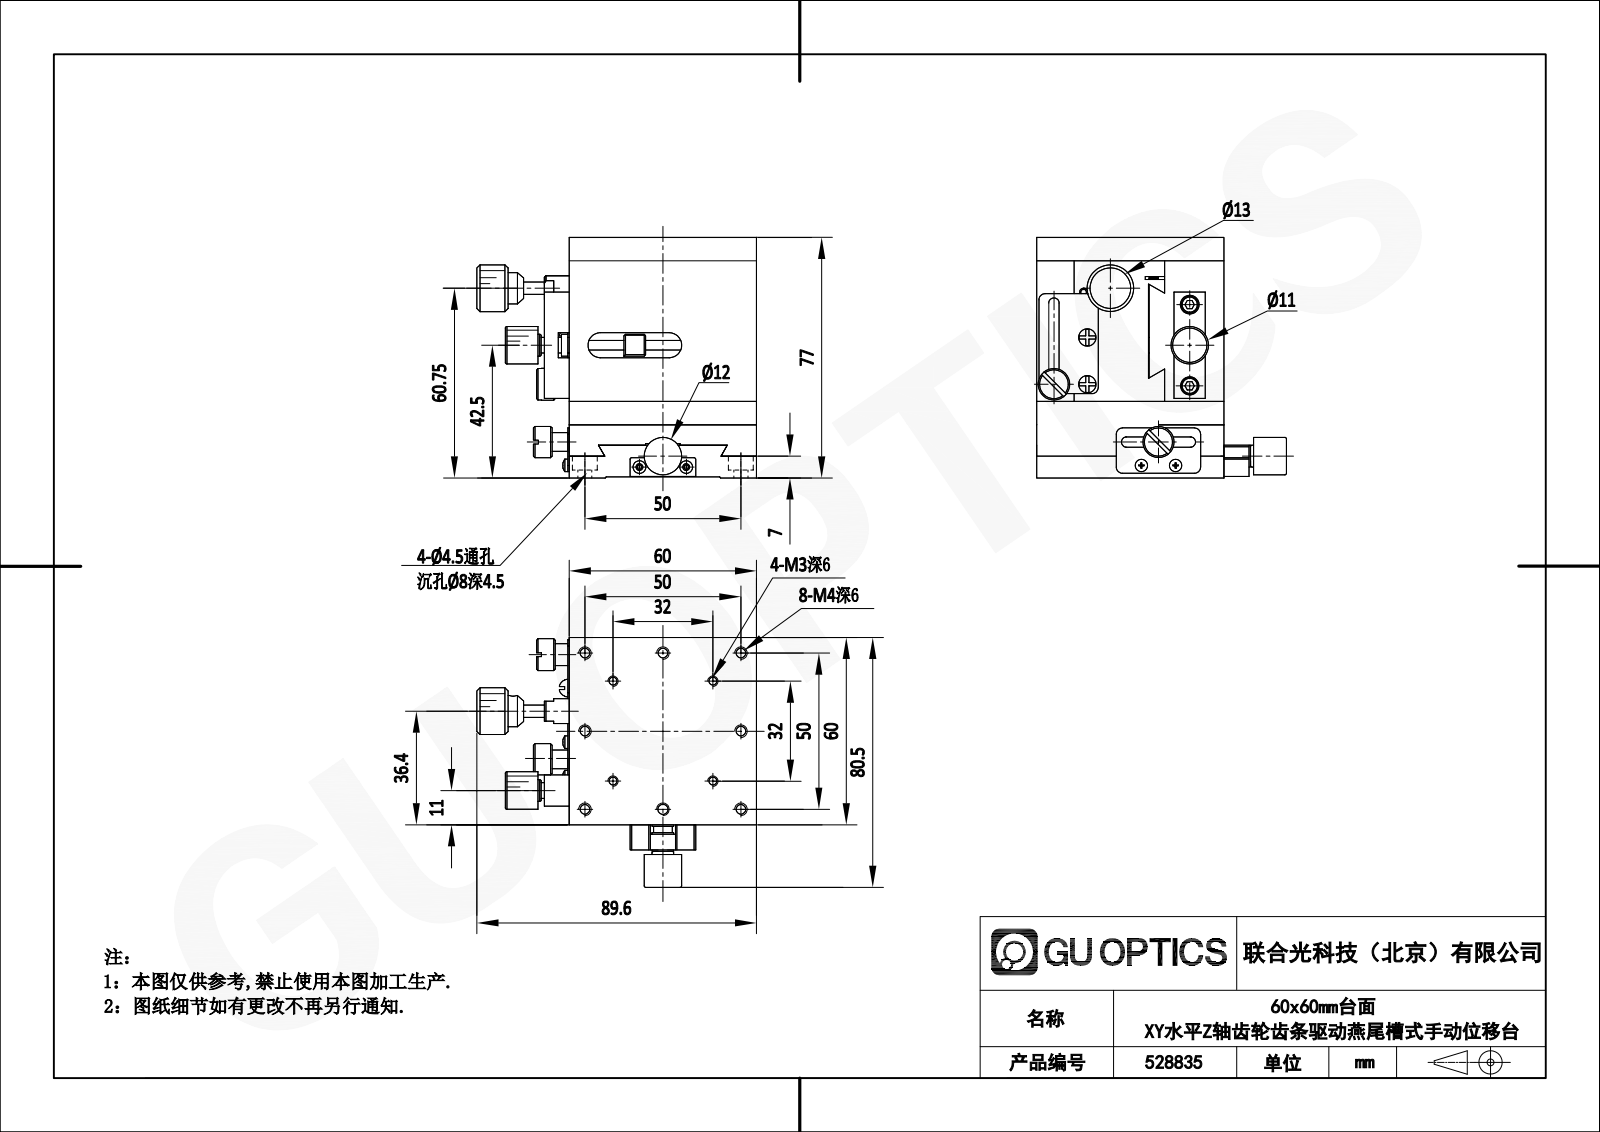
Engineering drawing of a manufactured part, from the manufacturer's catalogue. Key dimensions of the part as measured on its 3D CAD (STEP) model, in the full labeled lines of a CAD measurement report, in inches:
Part name (STEP PRODUCT): 528835
STEP written by: SolidWorks 2020 (CONFIG_CONTROL_DESIGN)
Units: inches
Bodies: 42 solids, 2534 faces (1478 planar, 392 cylindrical, 664 other)
Overall size (bounding box): 3.441 × 3.169 × 3.012
Volume: 16.17 in³ · Surface area: 153.9 in²
Round holes (diameter × count): ⌀0.098 ×35, ⌀0.13 ×13, ⌀0.177 ×9, ⌀0.315 ×8, ⌀0.161 ×7, ⌀0.236 ×7, ⌀0.134 ×5, ⌀0.114 ×4, ⌀0.244 ×4, ⌀0.063 ×2, ⌀0.081 ×2, ⌀0.122 ×2
Round bosses / shafts (diameter × count): ⌀0.118 ×11, ⌀0.217 ×6, ⌀0.157 ×3, ⌀0.394 ×2, ⌀0.354 ×2, ⌀0.268 ×2, ⌀0.256 ×2, ⌀0.24 ×2
Partial cylindrical surfaces — rounded edges, fillets, slot ends (radius × count): R0.012 ×16, R0.217 ×6, R0.079 ×5, R0.059 ×4, R0.126 ×4, R0.063 ×2, R0.071 ×2, R0.089 ×2
Main face-to-face distances: 2.047, 0.295, 2.362, 1.752, 0.846, 0.531, 0.177, 2.343, 0.858, 0.669
Hole centre spacings: 0.984, 0.63, 0.723, 1.26, 1.653, 1.733, 1.969, 2.201
